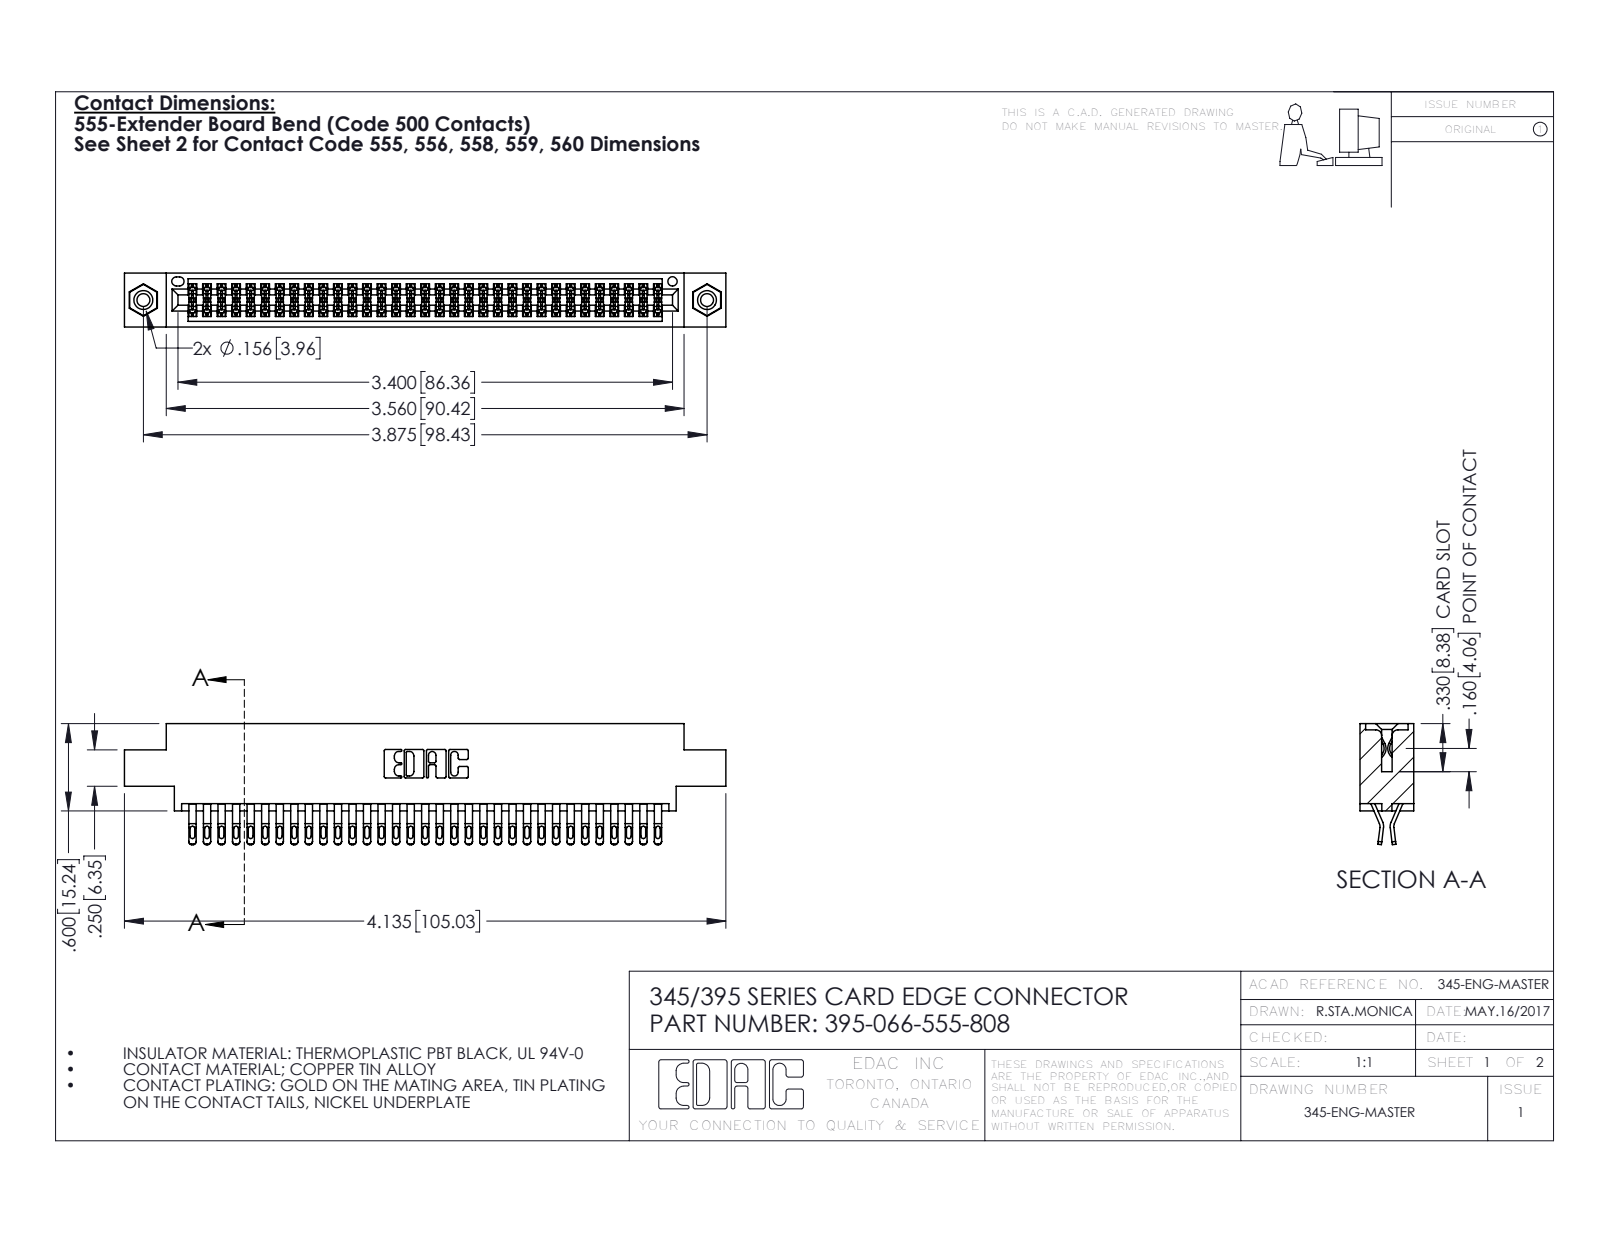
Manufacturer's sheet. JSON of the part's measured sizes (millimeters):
{"part_name": "345-292-001_555 Tail; 345-250-001_345-250-003-102; 345 Part_0.170 Offset - 0.156 Dia-TI; 395-066-555-808", "step_written_by": "SolidWorks 2016 (CONFIG_CONTROL_DESIGN)", "units": "millimeters", "bodies": {"solids": 69, "faces": 3886, "planar": 2162, "cylindrical": 1708, "other": 16}, "overall_size": [105, 21.1, 9.4], "volume_mm3": 10200, "surface_area_mm2": 15710, "round_holes": [[2.3, 2], [3.2, 2], [4, 2], [1.6, 1]], "round_bosses_or_shafts": [[3.9, 2]], "partial_cylinders_radius": [[0.4, 165], [0.5, 132], [0.2, 99], [0.3, 22], [0.2, 6], [0.8, 6], [0.7, 3], [0.3, 2]], "face_to_face_distances": [1.8, 7.6, 9.4, 0.6, 5.1, 2.5, 6.9, 5.7, 4.4, 3.8], "hole_center_spacings": [6.9, 92.5, 98.4]}
